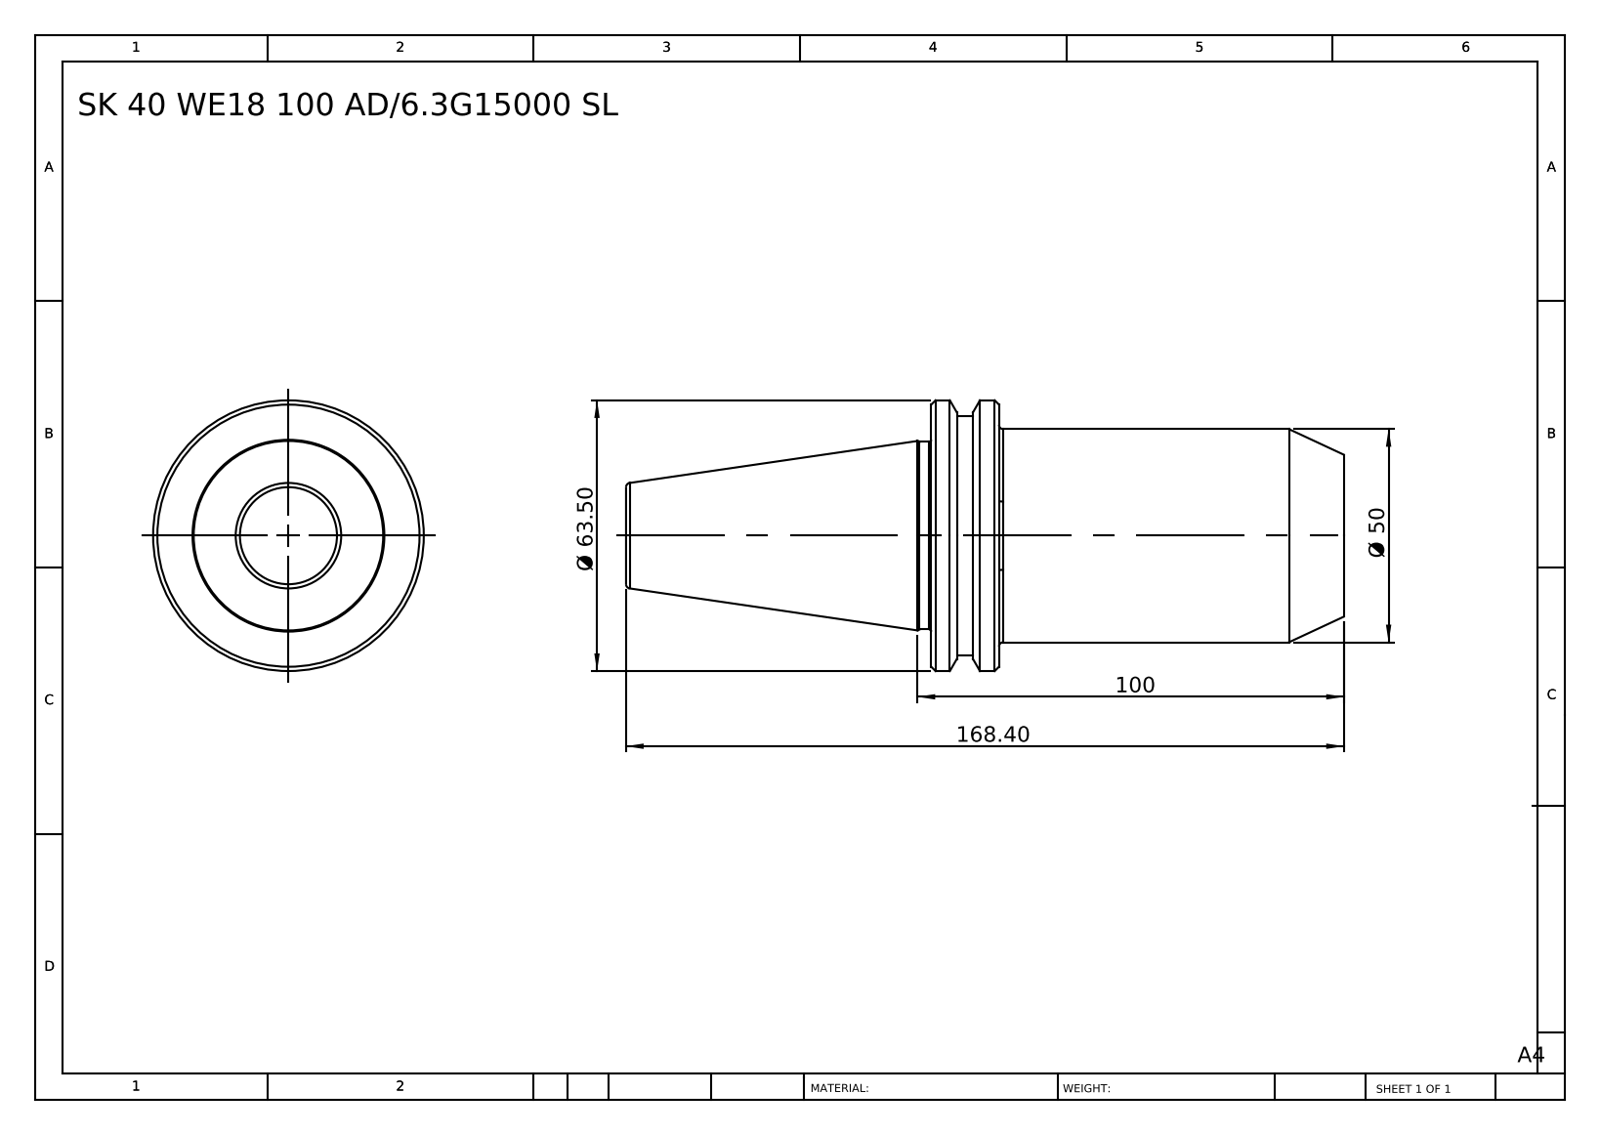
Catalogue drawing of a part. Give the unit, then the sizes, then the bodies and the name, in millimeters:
Units: millimetres
Overall size (bounding box): 168.4 × 63.5 × 63.5
Round bosses / shafts (diameter × count): ⌀63.5 ×1, ⌀56 ×1, ⌀50 ×1, ⌀44 ×1
Main face-to-face distances: 96.8, 80.9, 15.9, 168.4, 87.5, 71.6, 87, 6.1, 9.8, 81.4
Volume: 270 408 mm³ · Surface area: 28 695 mm²
Bodies: 1 solid, 36 faces (6 planar, 10 cylindrical, 20 other)
Part name (STEP PRODUCT): SK40 WE18 100 AD-6.3G15000 SL
STEP written by: SolidWorks 2014 (CONFIG_CONTROL_DESIGN)
